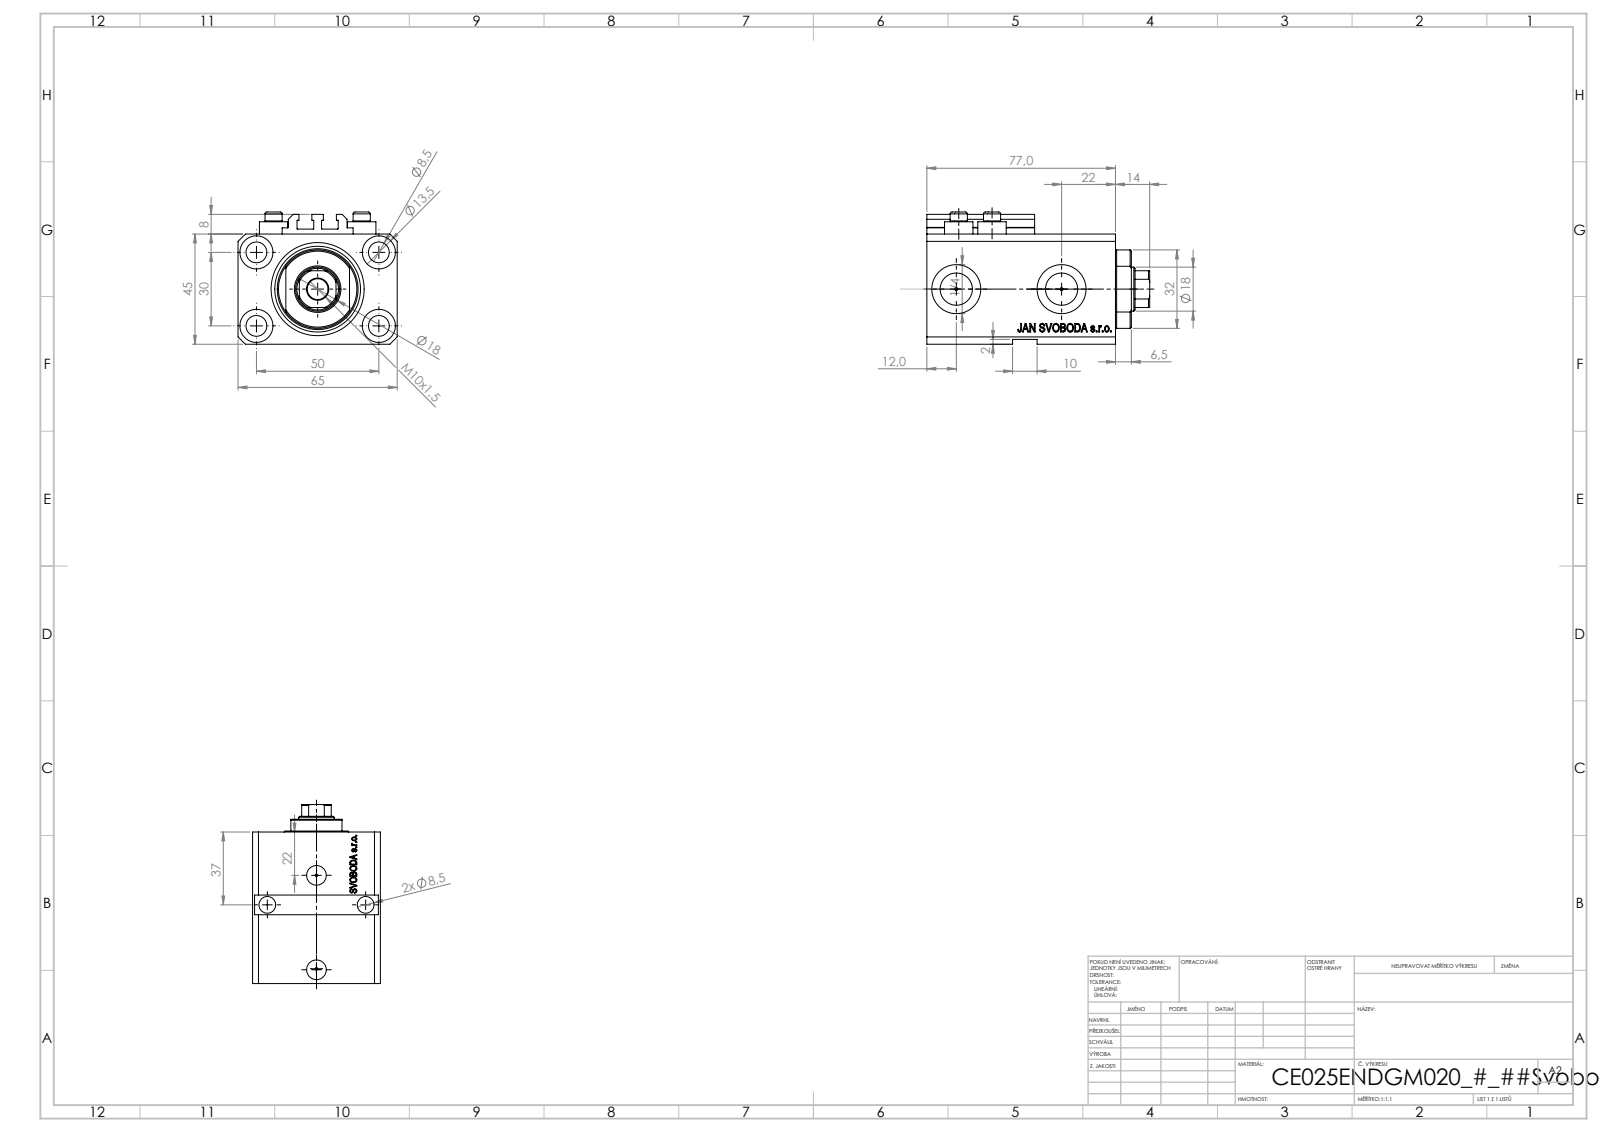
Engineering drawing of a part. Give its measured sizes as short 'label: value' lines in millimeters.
name: V250CE_C_VCP; V250CE_E_Body; ALLEN BOLT V250CE; V250CE_VC_E
written by: SolidWorks 2019 (CONFIG_CONTROL_DESIGN)
unit: mm
bodies: 8 solids, 1083 faces (515 planar, 138 cylindrical, 430 other)
size: 91 × 65 × 54
volume: 196 158 mm³; area: 60 322 mm²
holes: 7× ⌀8.5, 4× ⌀1.25, 4× ⌀4, 4× ⌀13.5, 2× ⌀10, 2× ⌀13.16, 2× ⌀20, 1× ⌀18, 1× ⌀25, 1× ⌀38
bosses: 4× ⌀11.6, 4× ⌀7
rounds: 10× R0.2, 1× R8.5, 1× R16
face distances: 45, 65, 63, 14, 77, 2, 6.9, 56.1, 70.1, 47
hole spacings: 29.15, 50, 13.6, 15.12, 18.81, 18.97, 26.22, 26.61
